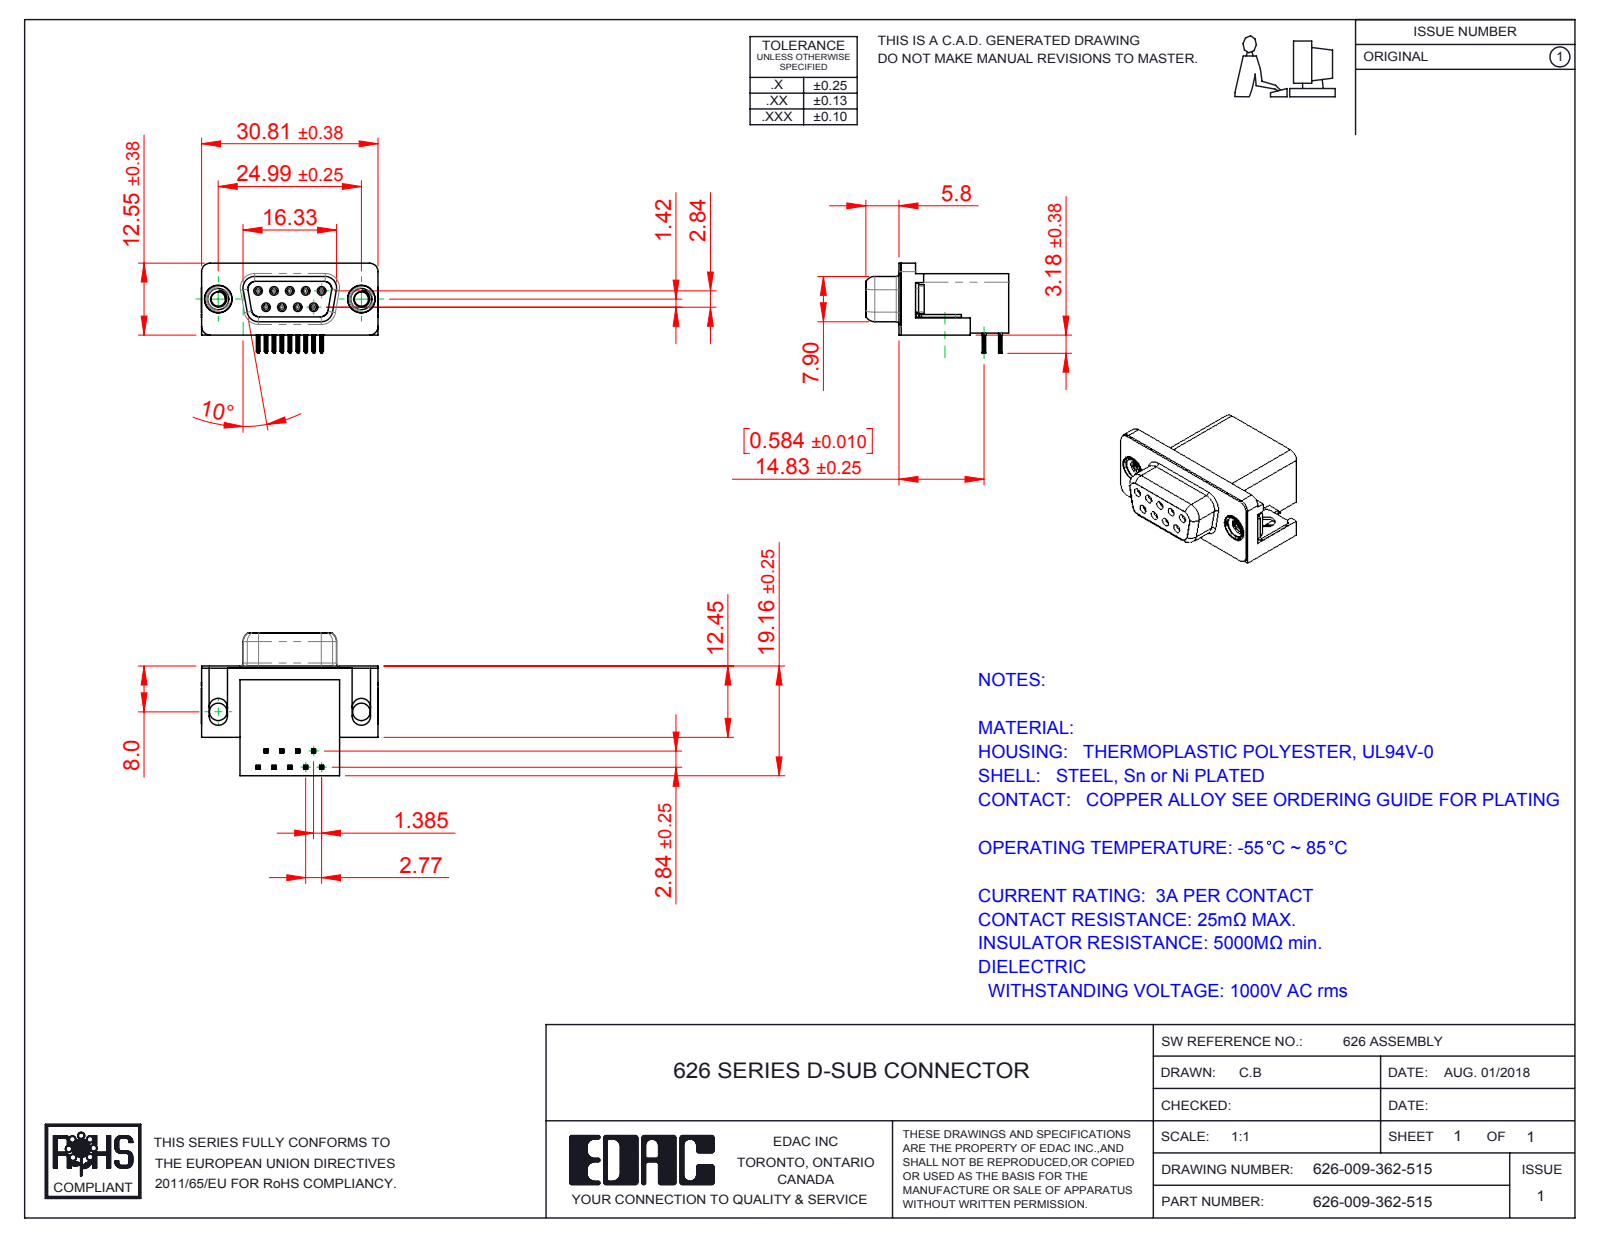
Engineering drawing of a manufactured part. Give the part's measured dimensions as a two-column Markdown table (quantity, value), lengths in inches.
| quantity | value |
| --- | --- |
| part name | 626 Contact Bottom; 626-009-362-515; 626 Shell_9 Socket; 626 Contact Top (+3 more) |
| STEP written by | SolidWorks 2016 (CONFIG_CONTROL_DESIGN) |
| units | inches |
| bodies | 15 solids, 1572 faces (684 planar, 420 cylindrical, 468 other) |
| overall size | 1.216 × 0.983 × 0.619 |
| volume | 0.303 in³ |
| surface area | 8.961 in² |
| round holes (diameter × count) | 0.031 × 9, 0.035 × 9, 0.098 × 2, 0.12 × 2, 0.157 × 2, 0.189 × 2, 0.197 × 2 |
| round bosses / shafts (diameter × count) | 0.047 × 9, 0.193 × 2, 0.187 × 2, 0.154 × 2 |
| partial cylindrical surfaces (radius × count) | 0.004 × 72, 0.006 × 36, 0.014 × 18, 0.039 × 18, 0.013 × 9, 0.01 × 8, 0.053 × 8, 0.063 × 8 |
| main face-to-face distances | 0.016, 0.407, 0.014, 0.739, 0.754, 0.114, 0.098, 0.244, 0.64, 0.02 |
| hole center spacings | 0.124, 0.109, 0.218, 0.198, 0.198, 0.327, 0.294, 0.295 |
